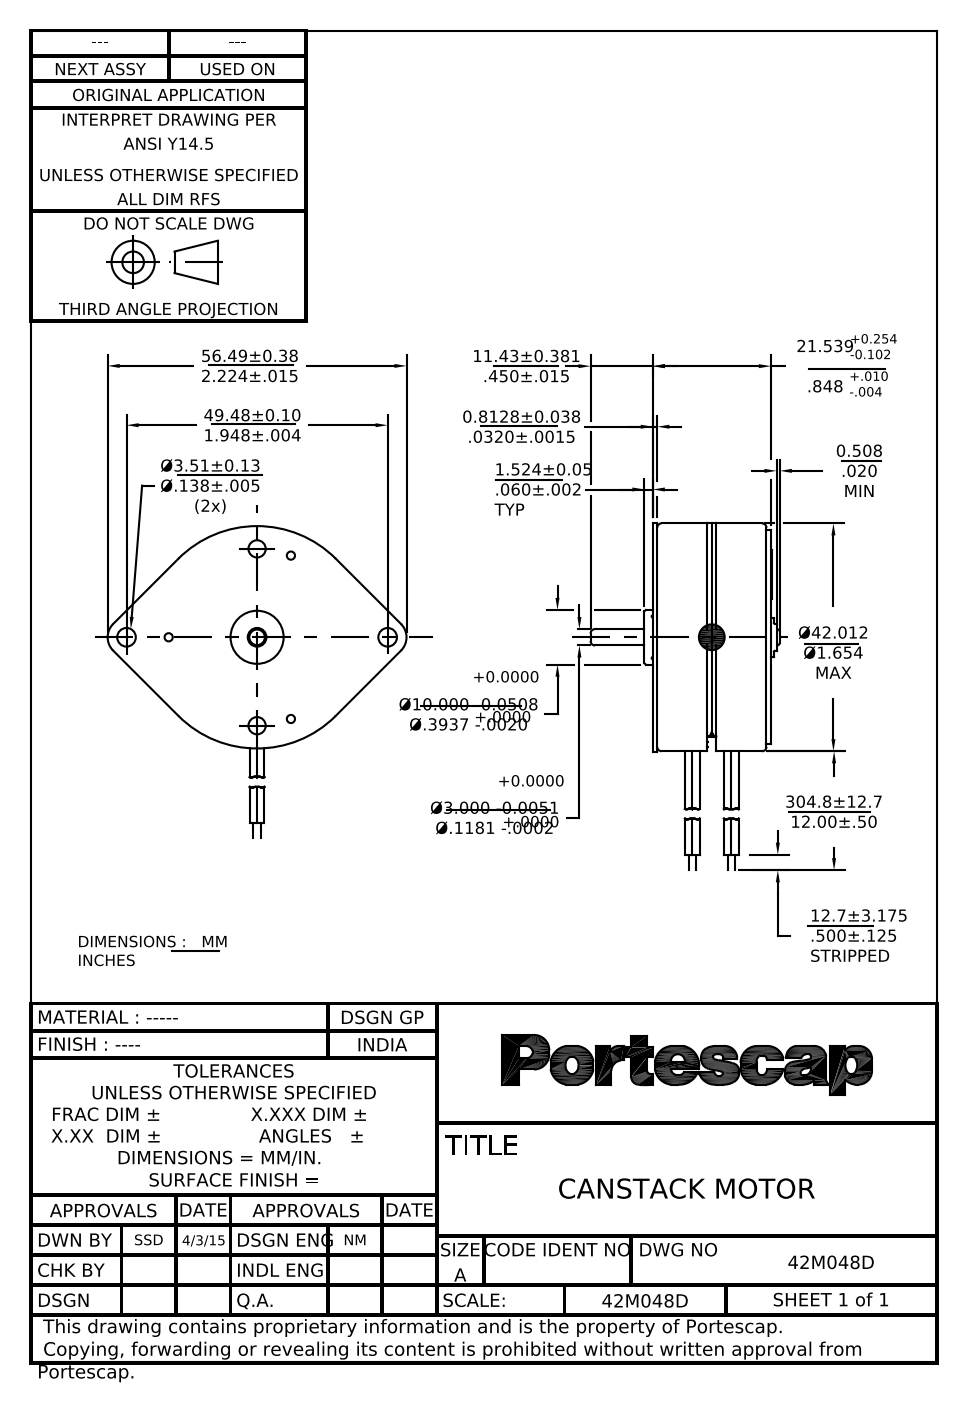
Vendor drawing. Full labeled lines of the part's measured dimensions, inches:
Part name (STEP PRODUCT): 053-6035-002_2; 150-5011-001_1; 585-5067-001_ASM_2_ASM; 012-5011-002_2 (+8 more)
STEP written by: PRO/ENGINEER BY PARAMETRIC TECHNOLOGY CORPORATION, 2014310 (CONFIG_CONTROL_DESIGN)
Units: inches
Bodies: 16 solids, 396 faces (122 planar, 192 cylindrical, 82 other)
Overall size (bounding box): 2.225 × 1.949 × 1.359
Volume: 1.985 in³ · Surface area: 36.81 in²
Round holes (diameter × count): ⌀0.138 ×6, ⌀0.104 ×4, ⌀0.128 ×2, ⌀0.128 ×2, ⌀0.118 ×1, ⌀0.286 ×1, ⌀0.286 ×1, ⌀1.1 ×1, ⌀1.109 ×1, ⌀1.518 ×1, ⌀1.58 ×1
Round bosses / shafts (diameter × count): ⌀0.053 ×6, ⌀0.136 ×2, ⌀1.644 ×1, ⌀1.545 ×1, ⌀1.54 ×1, ⌀1.478 ×1, ⌀0.394 ×1, ⌀0.285 ×1
Partial cylindrical surfaces — rounded edges, fillets, slot ends (radius × count): R0.023 ×8, R0.022 ×4, R0.031 ×4, R0.125 ×2, R0.138 ×2, R0.791 ×1, R0.822 ×1, R0.827 ×1
Main face-to-face distances: 0.032, 0.394, 0.788, 0.426, 0.82, 0.362, 0.458, 0.064, 0.852, 0.788
Hole centre spacings: 0.333, 0.63, 0.856, 1.174, 1.243, 1.4, 0.63, 0.656
